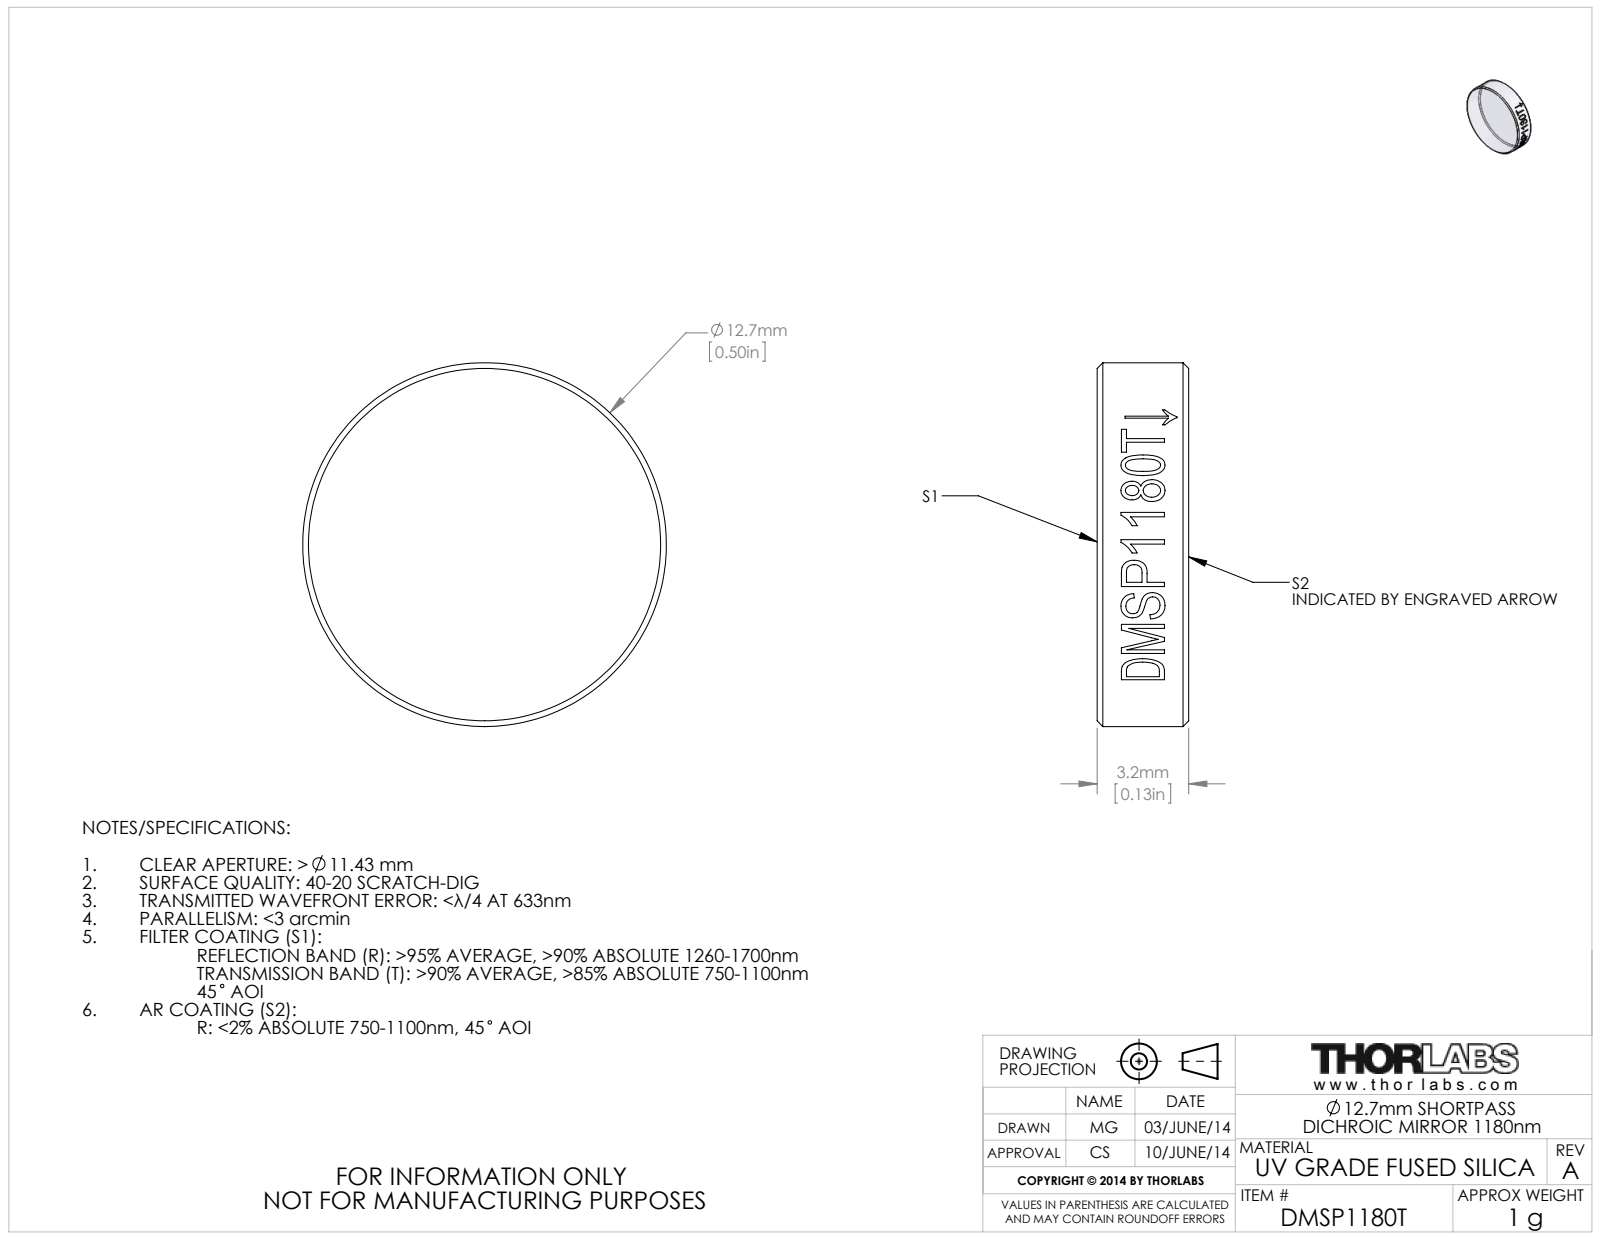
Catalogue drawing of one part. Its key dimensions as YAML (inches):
part_name: "TTN028296-E0W"
step_written_by: "SolidWorks 2012 (CONFIG_CONTROL_DESIGN)"
units: inches
bodies: {solids: 1, faces: 23, planar: 2, cylindrical: 17, other: 4}
overall_size: [0.5, 0.5, 0.126]
volume: 0.025
surface_area: 0.577
round_bosses_or_shafts:
  - {diameter: 0.5, count: 1}
face_to_face_distances: [0.126]
